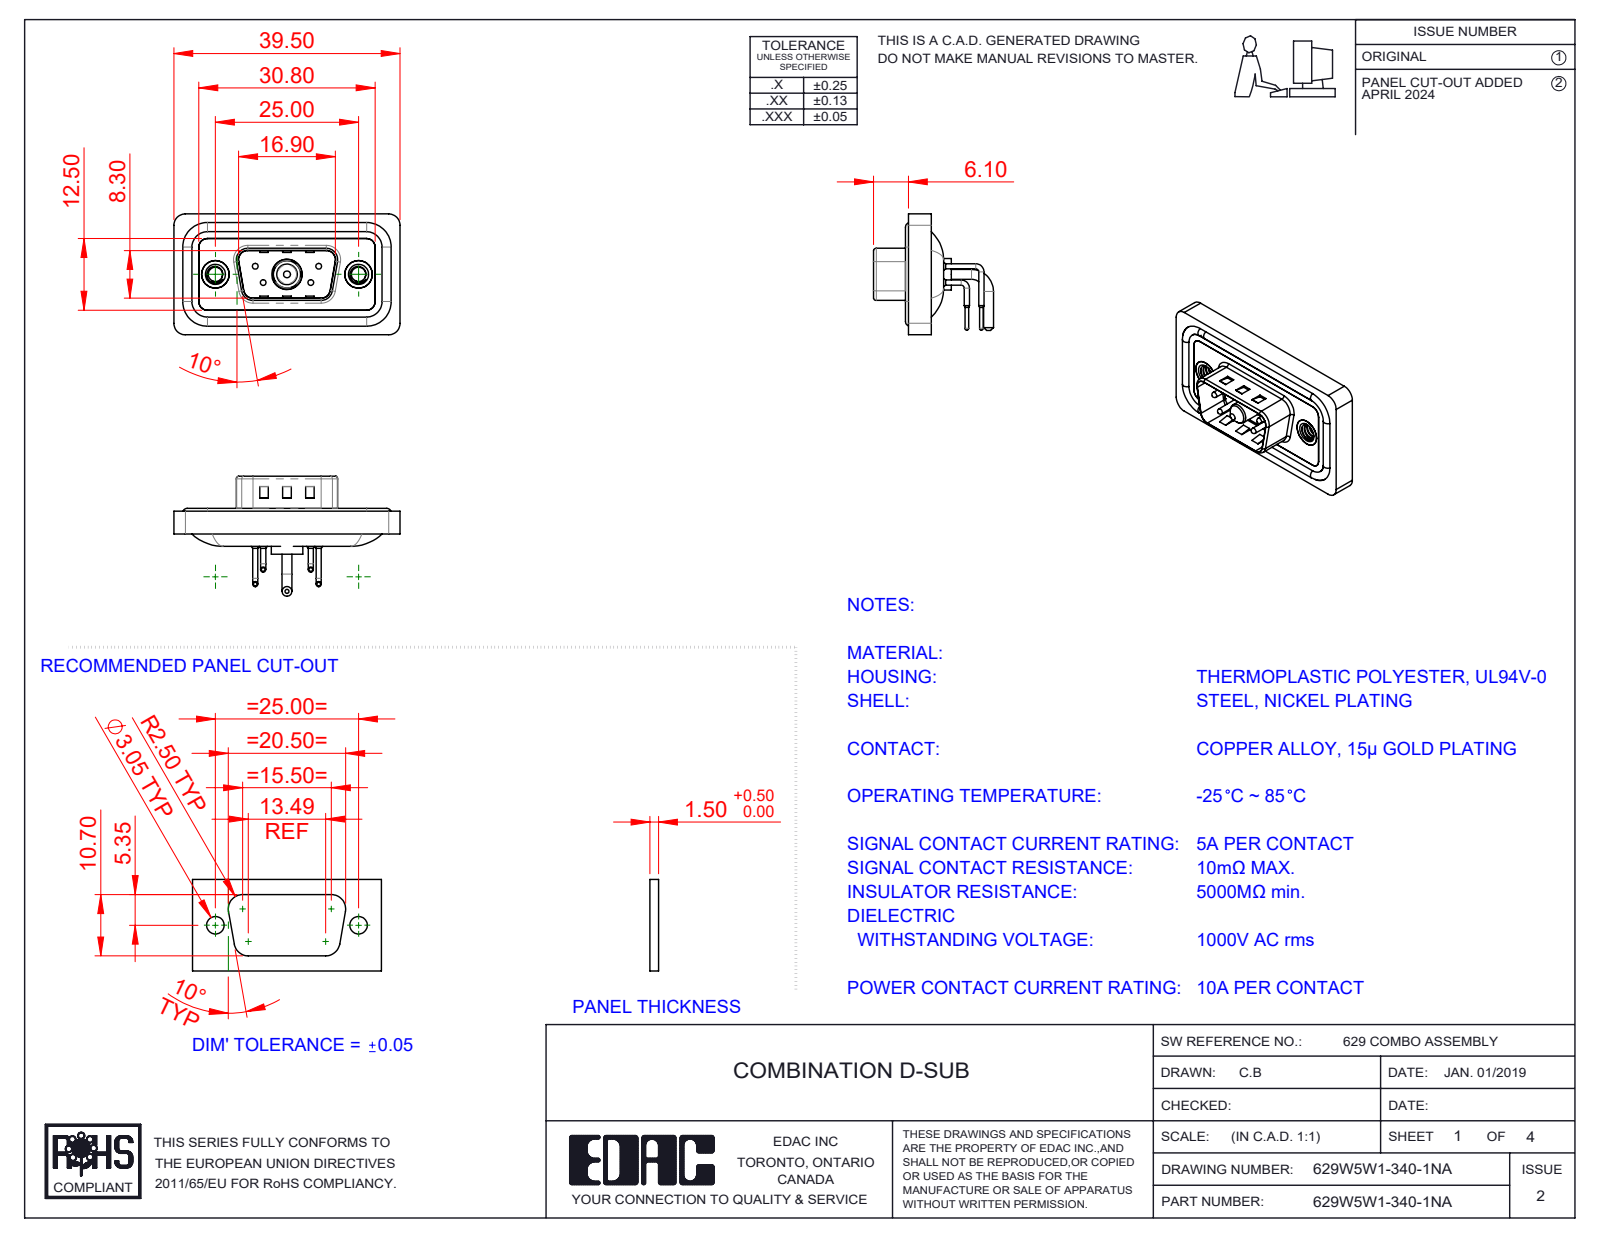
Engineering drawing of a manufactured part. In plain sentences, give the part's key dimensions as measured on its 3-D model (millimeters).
The part is named "629Combo Threaded Rivet_A; Power Pin_10A RA; 629Combo Contact Row 2; 629Combo Waterproof Housing_09 Contacts (+5 more)". Its 3-D file was written by "SolidWorks 2023 (CONFIG_CONTROL_DESIGN)". It is 13 solids with 888 faces: 411 planar, 343 cylindrical and 134 other. Overall it measures 39.5 by 21.1 by 20.95 millimeters. Its volume is 4 422 cubic millimeters and its surface area 7 116 square millimeters. Round holes: 4 of diameter 0.75, 4 of diameter 1.6, 4 of diameter 2, 2 of diameter 2.5, 2 of diameter 4, 2 of diameter 4.8, 2 of diameter 5, 1 of diameter 4.85, 1 of diameter 5.3. Round bosses or shafts: 8 of diameter 0.9, 4 of diameter 1.6, 4 of diameter 1.5, 4 of diameter 1, 4 of diameter 0.65, 2 of diameter 4.9, 2 of diameter 1.7, 1 of diameter 5.5. Partial cylindrical surfaces (rounded edges, fillets, slot ends): 18 of radius 1.5, 18 of radius 2, 8 of radius 0.5, 8 of radius 1.6, 4 of radius 0.25, 4 of radius 0.6, 4 of radius 0.65, 4 of radius 0.9. The main face-to-face distances are 0.4, 2.9, 1.1, 0.8, 2.1, 2.5, 1.6, 3.1, 1.5, 4.5. The hole center spacings are 3.16, 5.72, 7.1, 12.5, 18.1, 4.39, 4.4, 8.31.
